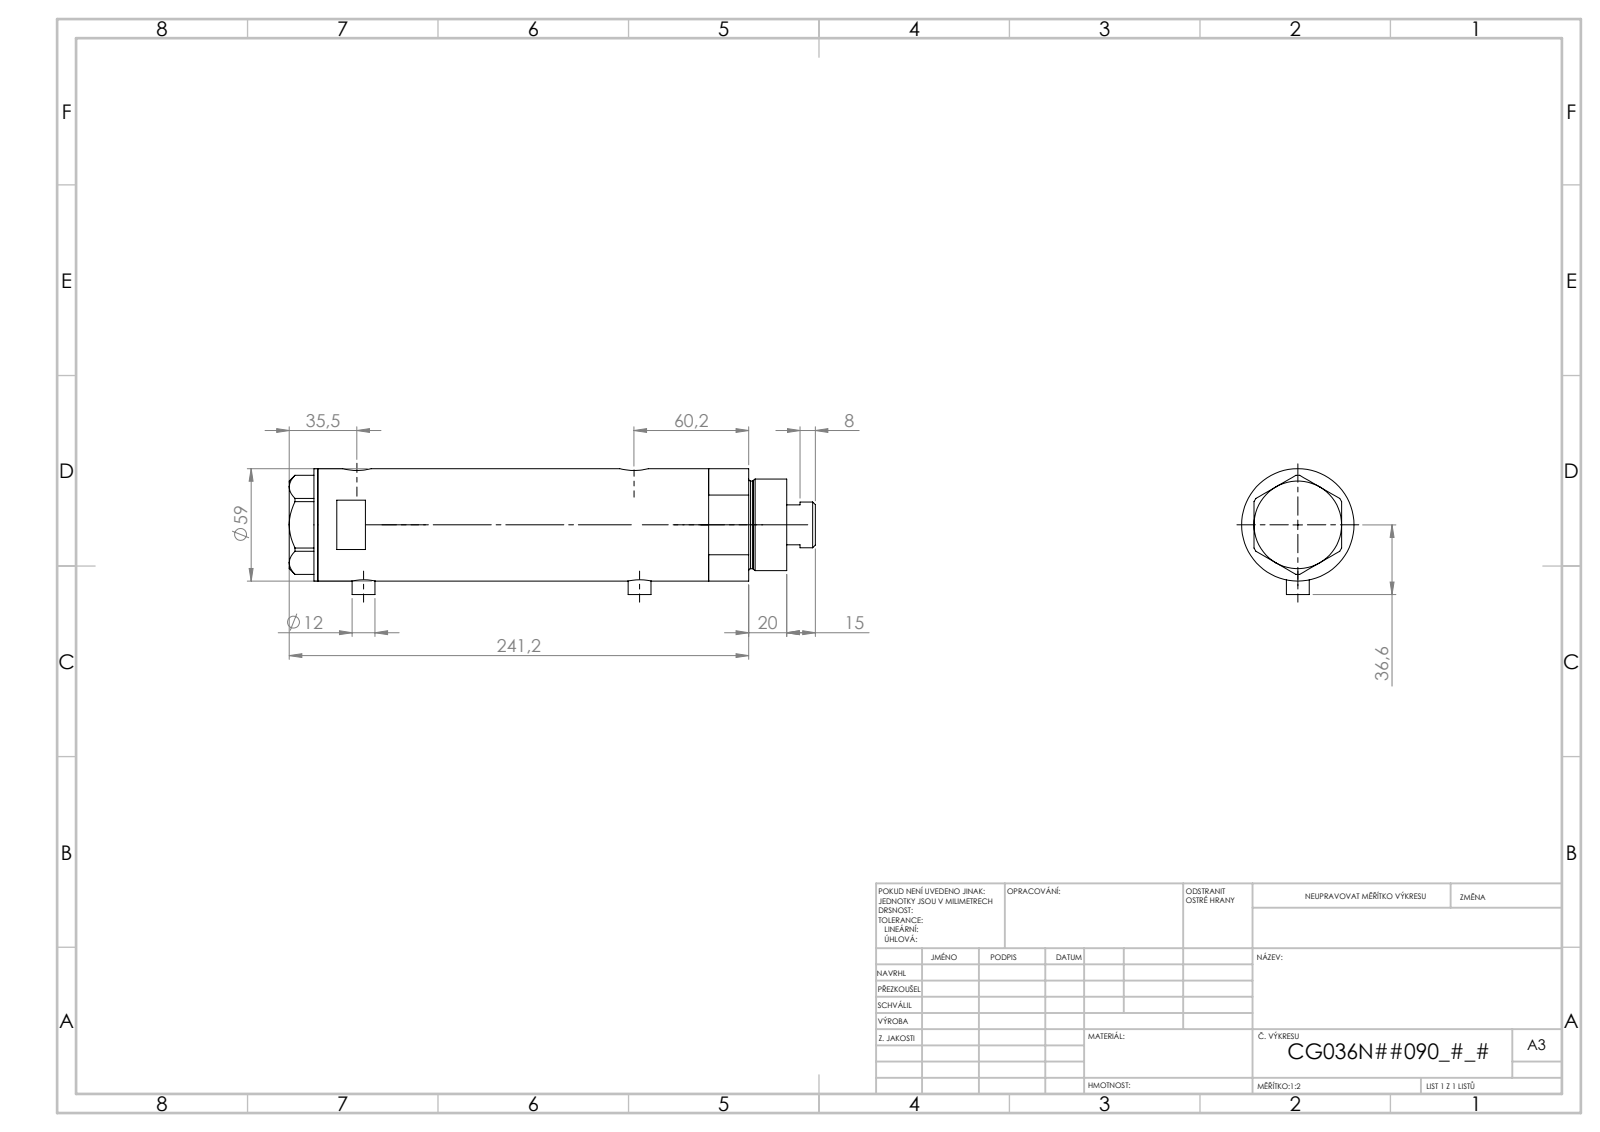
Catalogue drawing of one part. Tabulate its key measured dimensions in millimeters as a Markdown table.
| quantity | value |
| --- | --- |
| part name | V270CG_FRONT; V270CG_BACK; V270CG_VC; V270CG_MIDDLE |
| STEP written by | SolidWorks 2019 (CONFIG_CONTROL_DESIGN) |
| units | millimeters |
| bodies | 4 solids, 126 faces (53 planar, 53 cylindrical, 20 other) |
| overall size | 253.42 × 60.1 × 59 |
| volume | 569 769 mm³ |
| surface area | 115 822 mm² |
| round holes (diameter × count) | 5 × 2, 9.73 × 2, 12.5 × 2, 15 × 2, 8.5 × 1, 25 × 1, 26.5 × 1, 36 × 1, 40 × 1, 52 × 1 |
| round bosses / shafts (diameter × count) | 12 × 2, 59 × 1, 48 × 1, 46 × 1, 24 × 1 |
| main face-to-face distances | 147.34, 23.5, 123.84, 15, 38.5, 162.34, 238.42, 223.42, 199.92, 76.08 |
| hole center spacings | 2.9, 3.5, 122.15, 125.05, 125.65, 128.55, 2.89, 2.91 |
